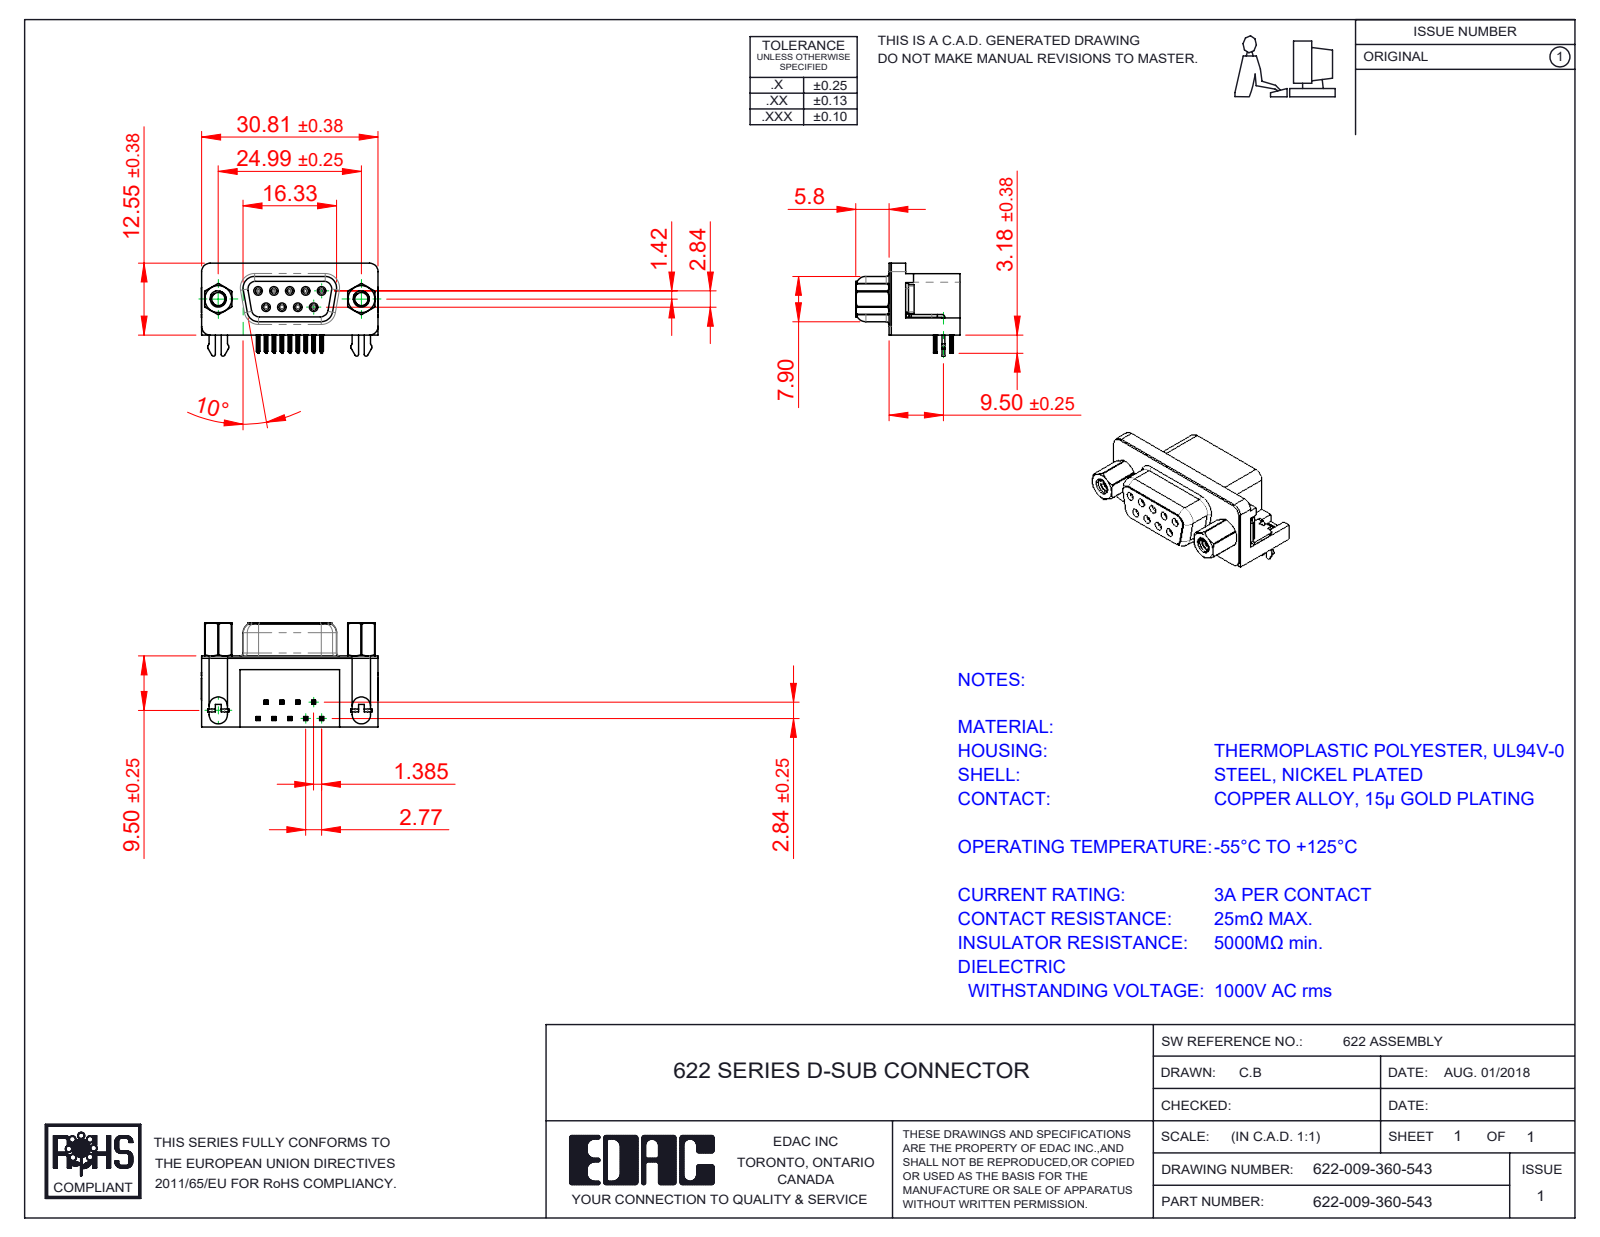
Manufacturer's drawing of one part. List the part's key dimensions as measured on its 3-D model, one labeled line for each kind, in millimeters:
Part name (STEP PRODUCT): 622 4 Prong Board Lock; 622 Housing_9 Socket; 622 4-40 Hex Standoff 5; 622-009-360-543 (+4 more)
STEP written by: SolidWorks 2016 (CONFIG_CONTROL_DESIGN)
Units: millimetres
Bodies: 17 solids, 1812 faces (748 planar, 486 cylindrical, 578 other)
Overall size (bounding box): 30.89 × 18.2 × 16.25
Volume: 3 937 mm³ · Surface area: 5 601 mm²
Round holes (diameter × count): ⌀0.8 ×9, ⌀0.9 ×9, ⌀2 ×2, ⌀2.26 ×2, ⌀2.29 ×2, ⌀4 ×2, ⌀4.8 ×2, ⌀5 ×2
Round bosses / shafts (diameter × count): ⌀1.2 ×9, ⌀4.9 ×2, ⌀4.75 ×2, ⌀3.9 ×2, ⌀3 ×2, ⌀2.79 ×2
Partial cylindrical surfaces — rounded edges, fillets, slot ends (radius × count): R0.1 ×72, R0.15 ×36, R0.35 ×18, R1 ×18, R0.25 ×12, R0.34 ×9, R1.35 ×8, R1.6 ×8
Main face-to-face distances: 0.4, 12, 12.4, 6.2, 0.35, 2.9, 2.5, 5.8, 10.34, 9.5
Hole centre spacings: 3.16, 2.77, 5.54, 5.03, 5.04, 8.31, 7.48, 7.49
